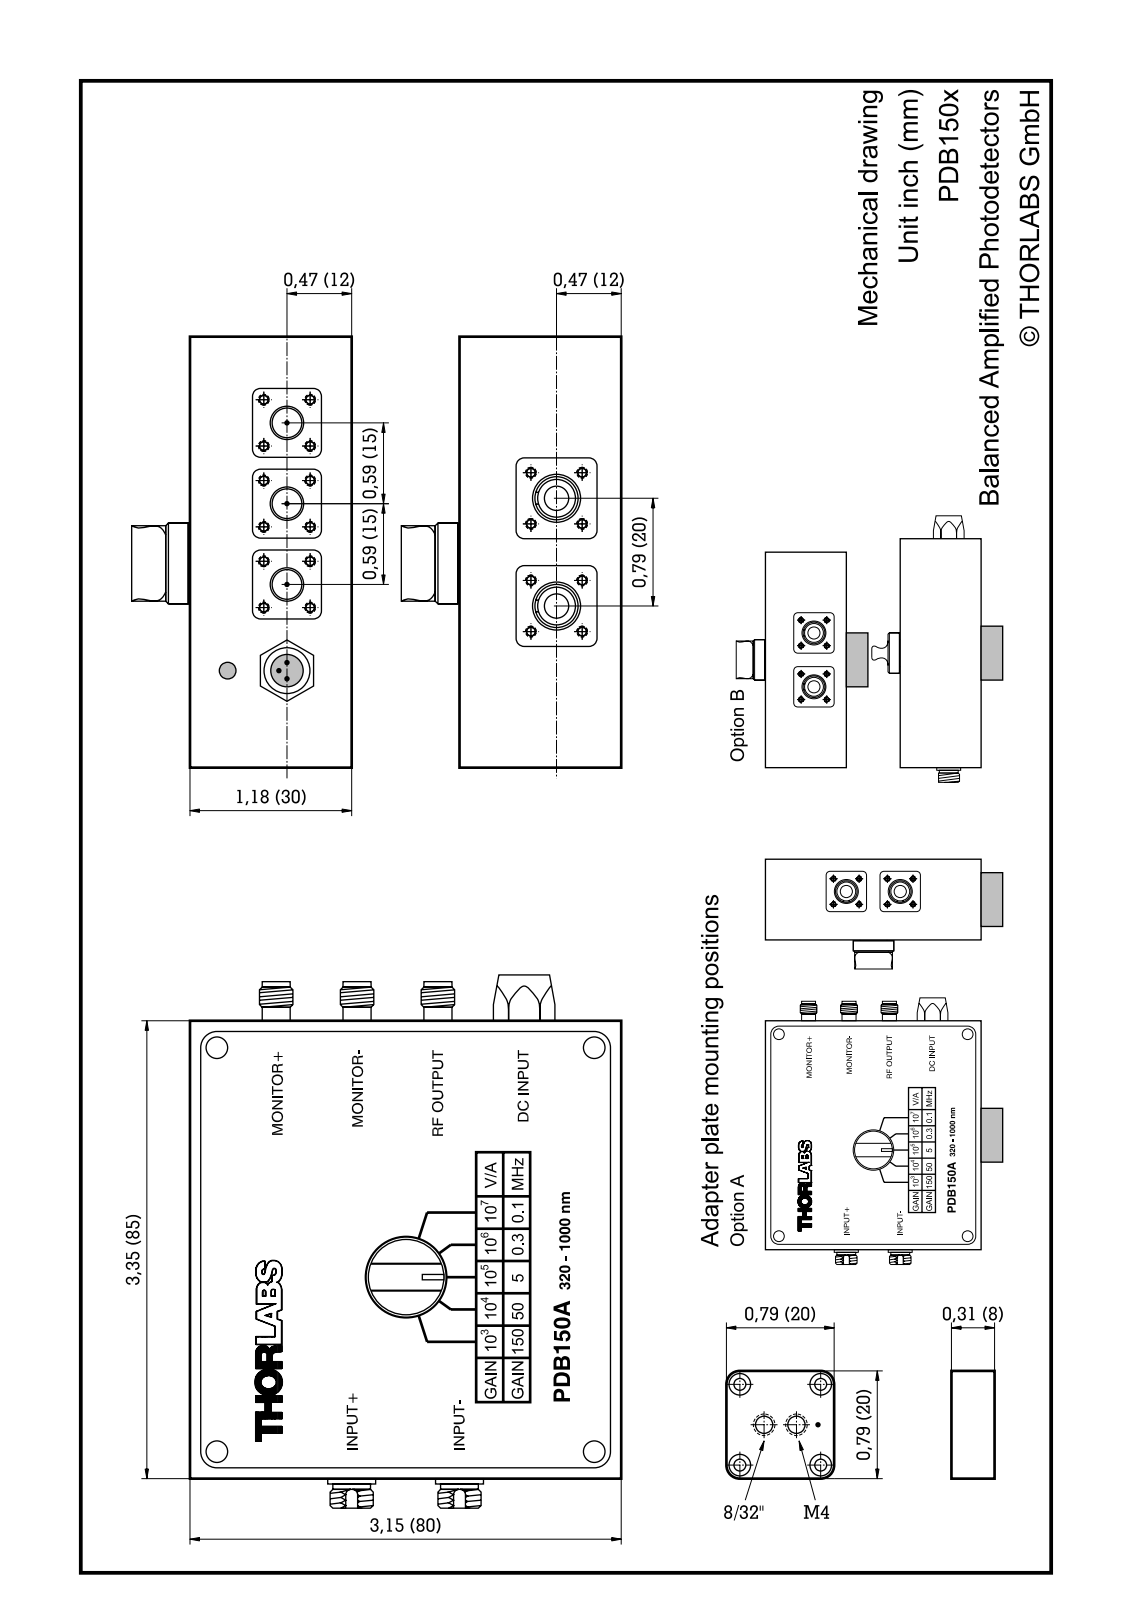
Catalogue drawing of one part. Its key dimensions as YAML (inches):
part_name: "13618-E0W"
step_written_by: "SolidWorks 2007 (AUTOMOTIVE_DESIGN)"
units: inches
bodies: {solids: 0, faces: 1428, planar: 827, cylindrical: 234, other: 367}
overall_size: [3.898, 3.465, 1.689]
round_holes:
  - {diameter: 0.173, count: 8}
  - {diameter: 0.157, count: 6}
  - {diameter: 0.039, count: 4}
  - {diameter: 0.315, count: 4}
  - {diameter: 0.161, count: 3}
  - {diameter: 0.185, count: 3}
  - {diameter: 0.062, count: 2}
  - {diameter: 0.062, count: 2}
  - {diameter: 0.098, count: 2}
  - {diameter: 0.244, count: 2}
  - {diameter: 0.079, count: 1}
  - {diameter: 0.122, count: 1}
round_bosses_or_shafts:
  - {diameter: 0.15, count: 28}
  - {diameter: 0.236, count: 4}
  - {diameter: 0.245, count: 3}
  - {diameter: 0.209, count: 3}
  - {diameter: 0.335, count: 2}
  - {diameter: 0.315, count: 2}
  - {diameter: 0.276, count: 2}
  - {diameter: 0.165, count: 2}
partial_cylinders:
  - {radius: 0.059, count: 20}
  - {radius: 0.118, count: 10}
  - {radius: 0.039, count: 8}
  - {radius: 0.098, count: 4}
  - {radius: 0.276, count: 1}
face_to_face_distances: [1.181, 3.15, 3.346, 0.079, 3.264, 0.083, 3.268, 3.185, 3.343, 0.315]
hole_center_spacings: [0.591, 0.264, 0.344, 0.373, 0.508, 0.835, 0.992, 1.602]
